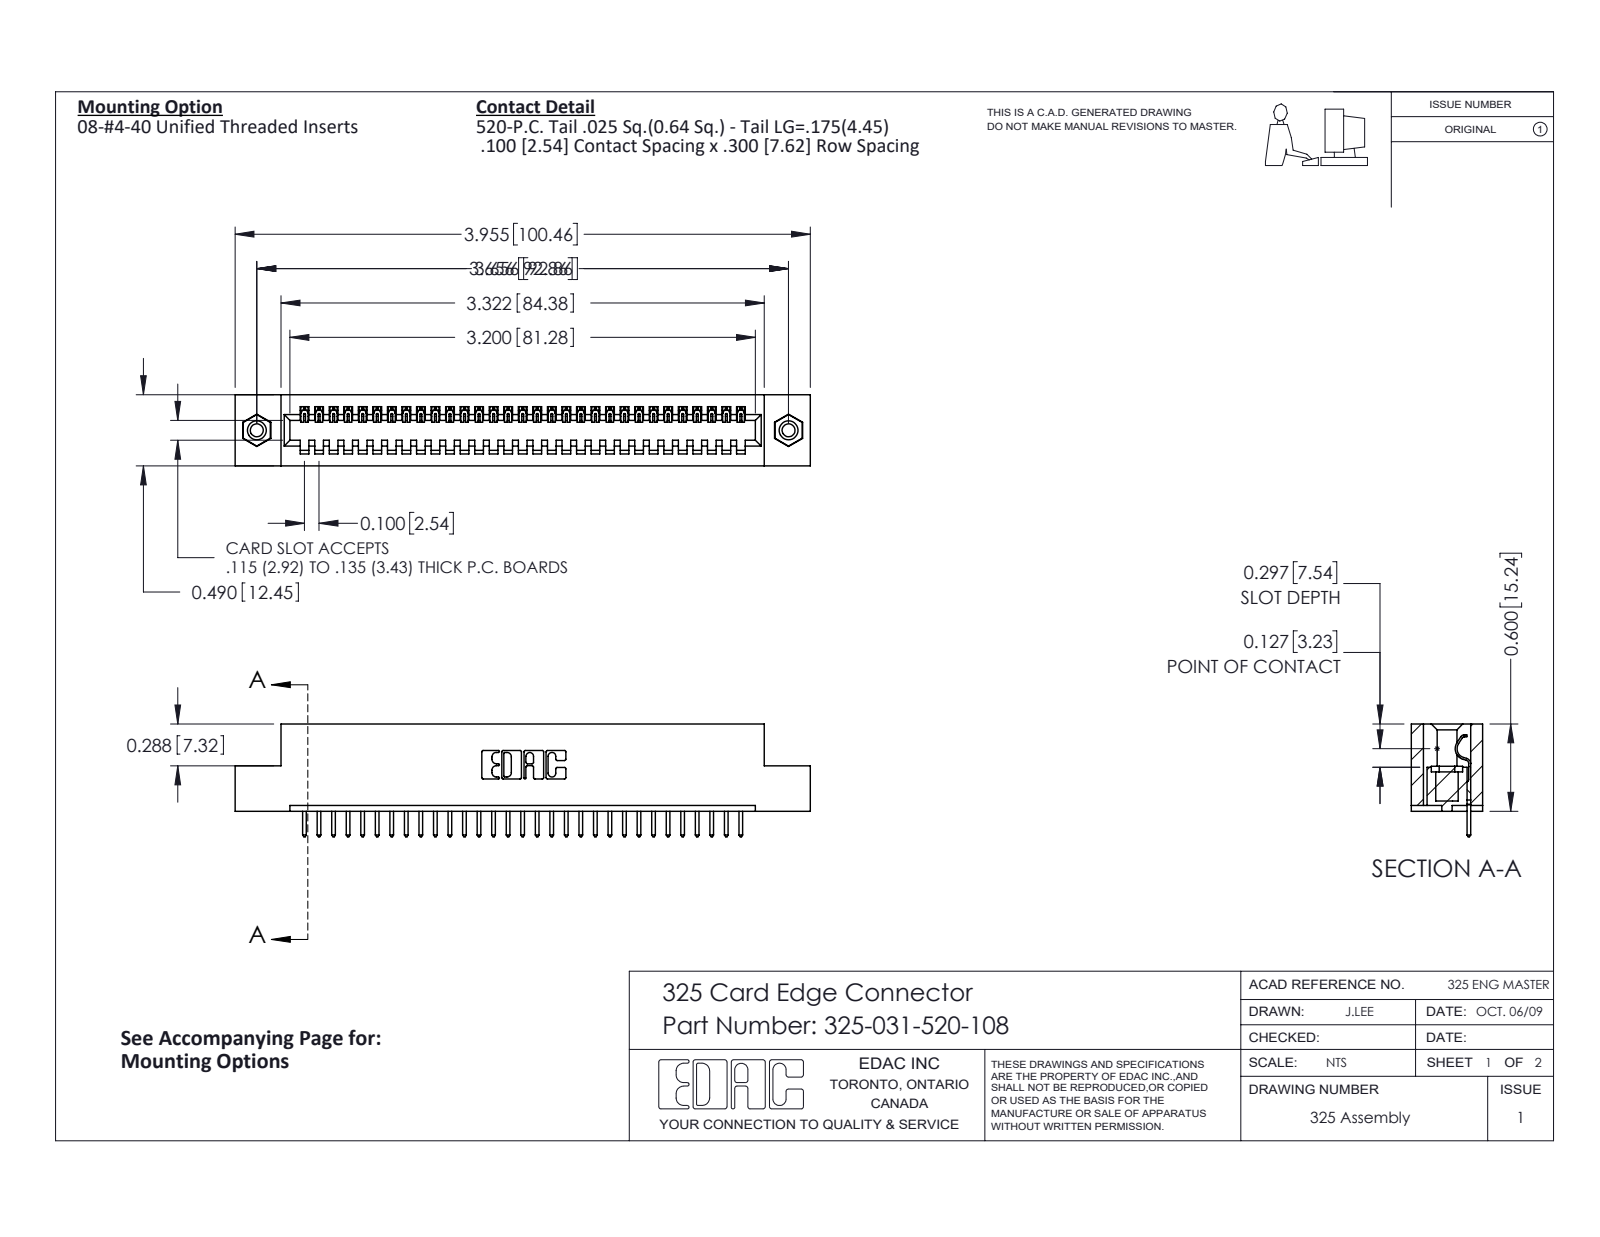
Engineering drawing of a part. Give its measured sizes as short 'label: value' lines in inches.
name: 325-031-520-108; 345-250-001_345-250-003-102; 325-292-001_325-293-120; 325 Part_TI
written by: SolidWorks 2016 (CONFIG_CONTROL_DESIGN)
unit: in
bodies: 34 solids, 1972 faces (1404 planar, 552 cylindrical, 16 other)
size: 3.955 × 0.775 × 0.49
volume: 0.768 in³; area: 20.53 in²
holes: 2× ⌀0.089, 2× ⌀0.125, 2× ⌀0.16
bosses: 2× ⌀0.155
rounds: 62× R0.006, 62× R0.01, 22× R0.01, 6× R0.007, 6× R0.031, 3× R0.026, 1× R0.014, 1× R0.022
face distances: 0.083, 0.407, 0.49, 0.3, 0.107, 0.383, 0.025, 0.325, 0.04, 0.1
hole spacings: 3.656
